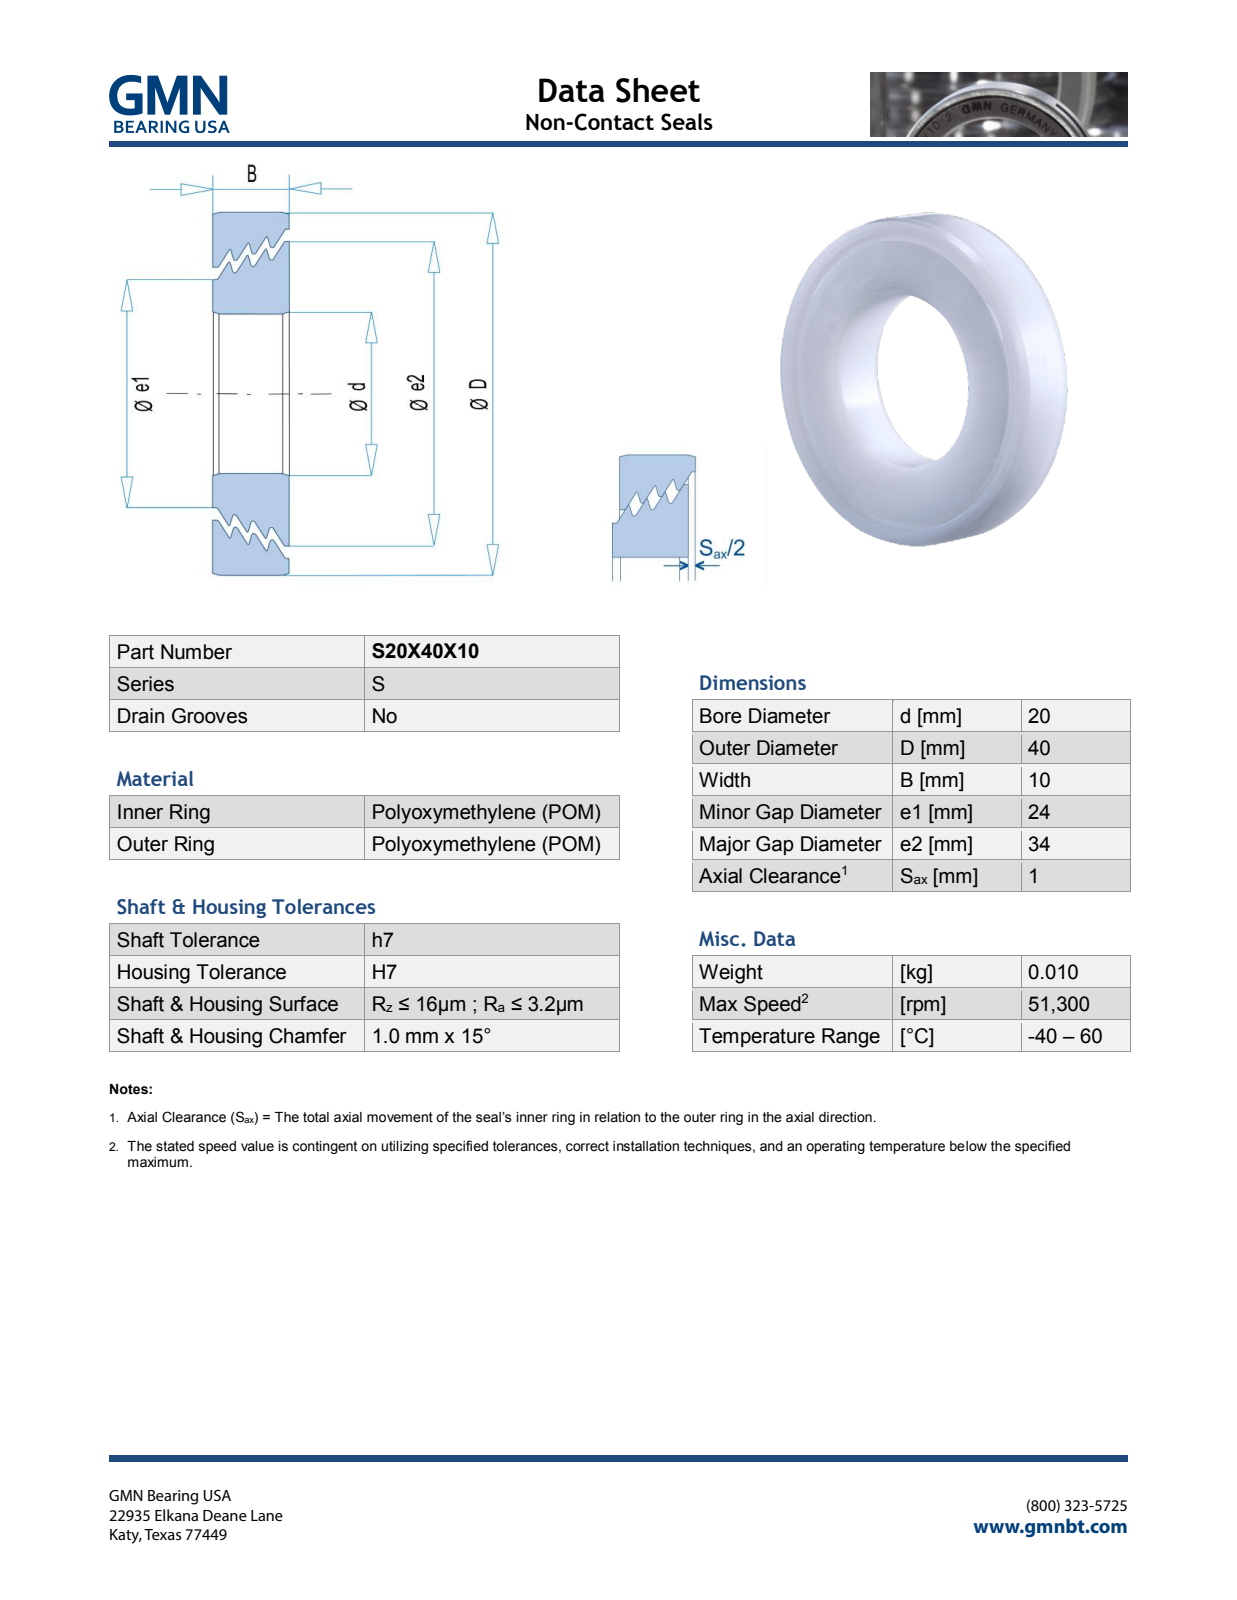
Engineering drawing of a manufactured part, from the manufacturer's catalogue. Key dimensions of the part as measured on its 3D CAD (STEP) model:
Part name (STEP PRODUCT): S20X40X10_PRT
STEP written by: PRO/ENGINEER BY PARAMETRIC TECHNOLOGY CORPORATION, 2013150 (AUTOMOTIVE_DESIGN)
Units: millimetres
Bodies: 2 solids, 630 faces (550 planar, 12 cylindrical, 68 other)
Overall size (bounding box): 40 × 40 × 10.07
Volume: 8 612 mm³ · Surface area: 7 406 mm²
Round holes (diameter × count): ⌀20 ×1, ⌀25.63 ×1, ⌀35.63 ×1
Round bosses / shafts (diameter × count): ⌀40 ×1, ⌀34 ×1, ⌀24 ×1
Main face-to-face distances: 10, 10.07, 1.83, 1.6, 1.3, 1.37, 1.53, 0.78, 1.84, 0.82
